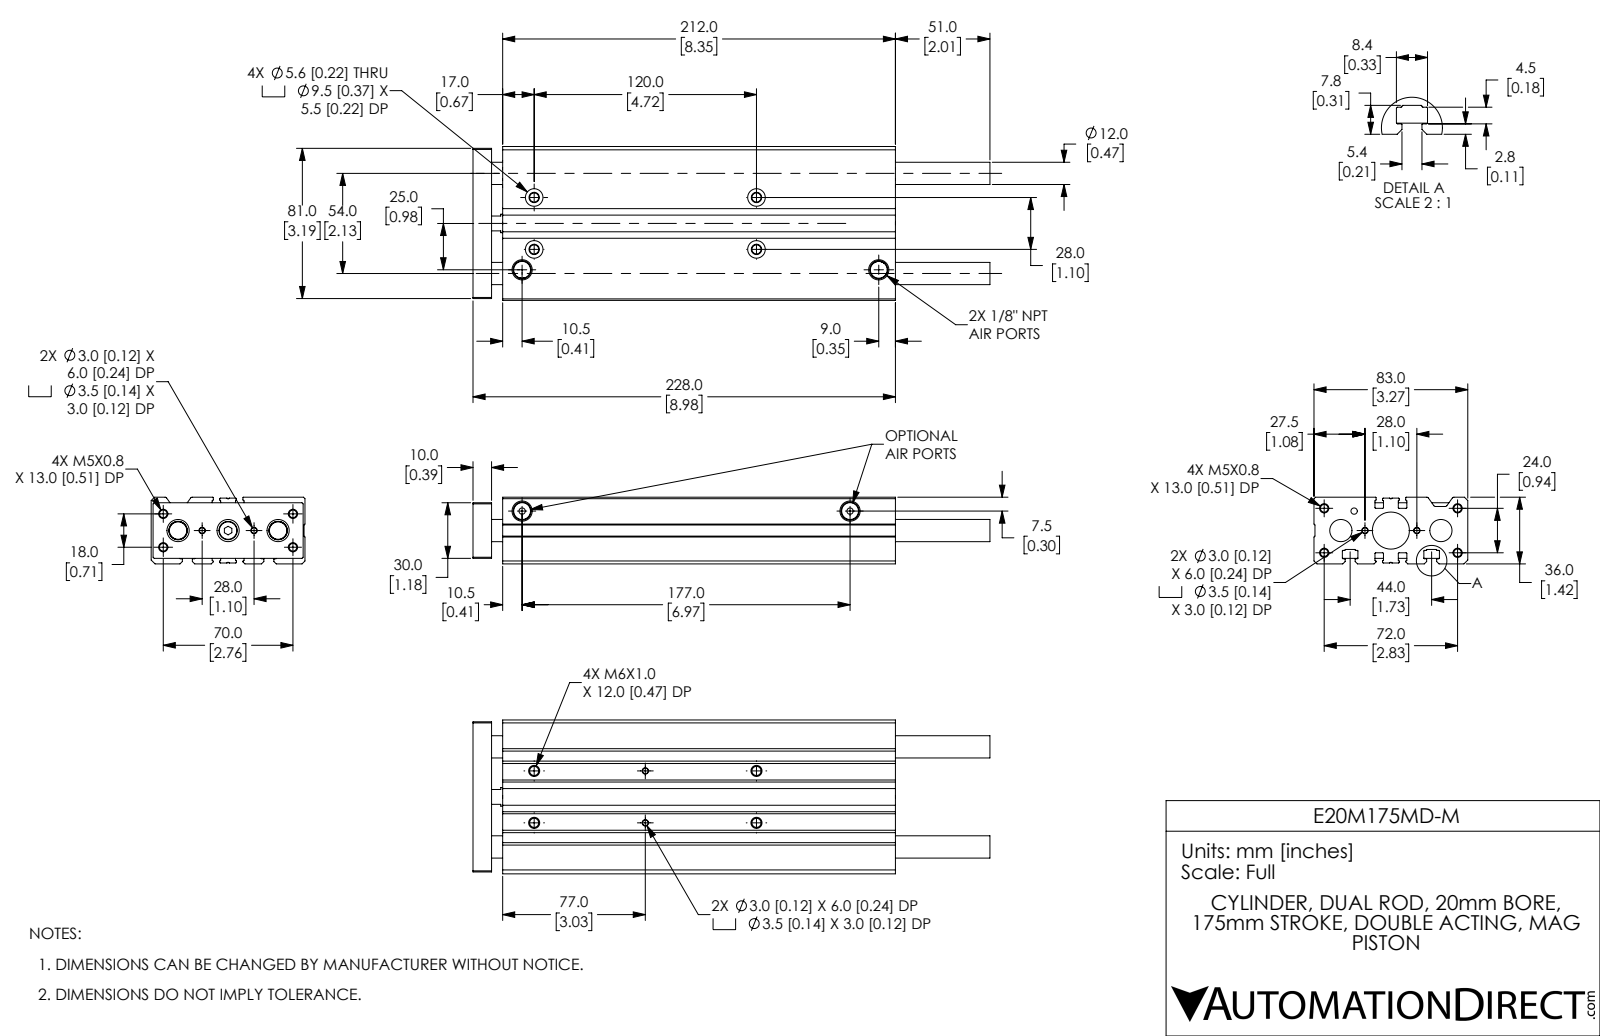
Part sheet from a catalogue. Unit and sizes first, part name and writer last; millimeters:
Units: millimetres
Overall size (bounding box): 279 × 83 × 36
Round holes (diameter × count): ⌀4.13 ×8, ⌀3 ×4, ⌀3.5 ×4, ⌀4.92 ×4, ⌀5.6 ×4, ⌀9.5 ×4, ⌀6 ×3, ⌀12 ×3, ⌀3.43 ×2, ⌀9.91 ×2, ⌀3.43 ×1, ⌀12 ×1
Round bosses / shafts (diameter × count): ⌀10 ×1, ⌀9.91 ×1
Partial cylindrical surfaces — rounded edges, fillets, slot ends (radius × count): R0.4 ×20, R0.2 ×18, R0.3 ×10, R0.25 ×8, R1 ×4
Main face-to-face distances: 36, 0.5, 83, 6, 30, 22.2, 45.5, 28.2, 3, 37.5
Hole centre spacings: 3.16, 12.04, 15, 21.02, 22.85, 25.06, 28, 36.14
Volume: 559 106 mm³ · Surface area: 146 982 mm²
Bodies: 5 solids, 404 faces (128 planar, 182 cylindrical, 94 other)
Part name (STEP PRODUCT): E20M175MD-M_BODY; E20M175MD-M_ENDPLATE; E20M175MD-M
STEP written by: SolidWorks 2019 (CONFIG_CONTROL_DESIGN)
